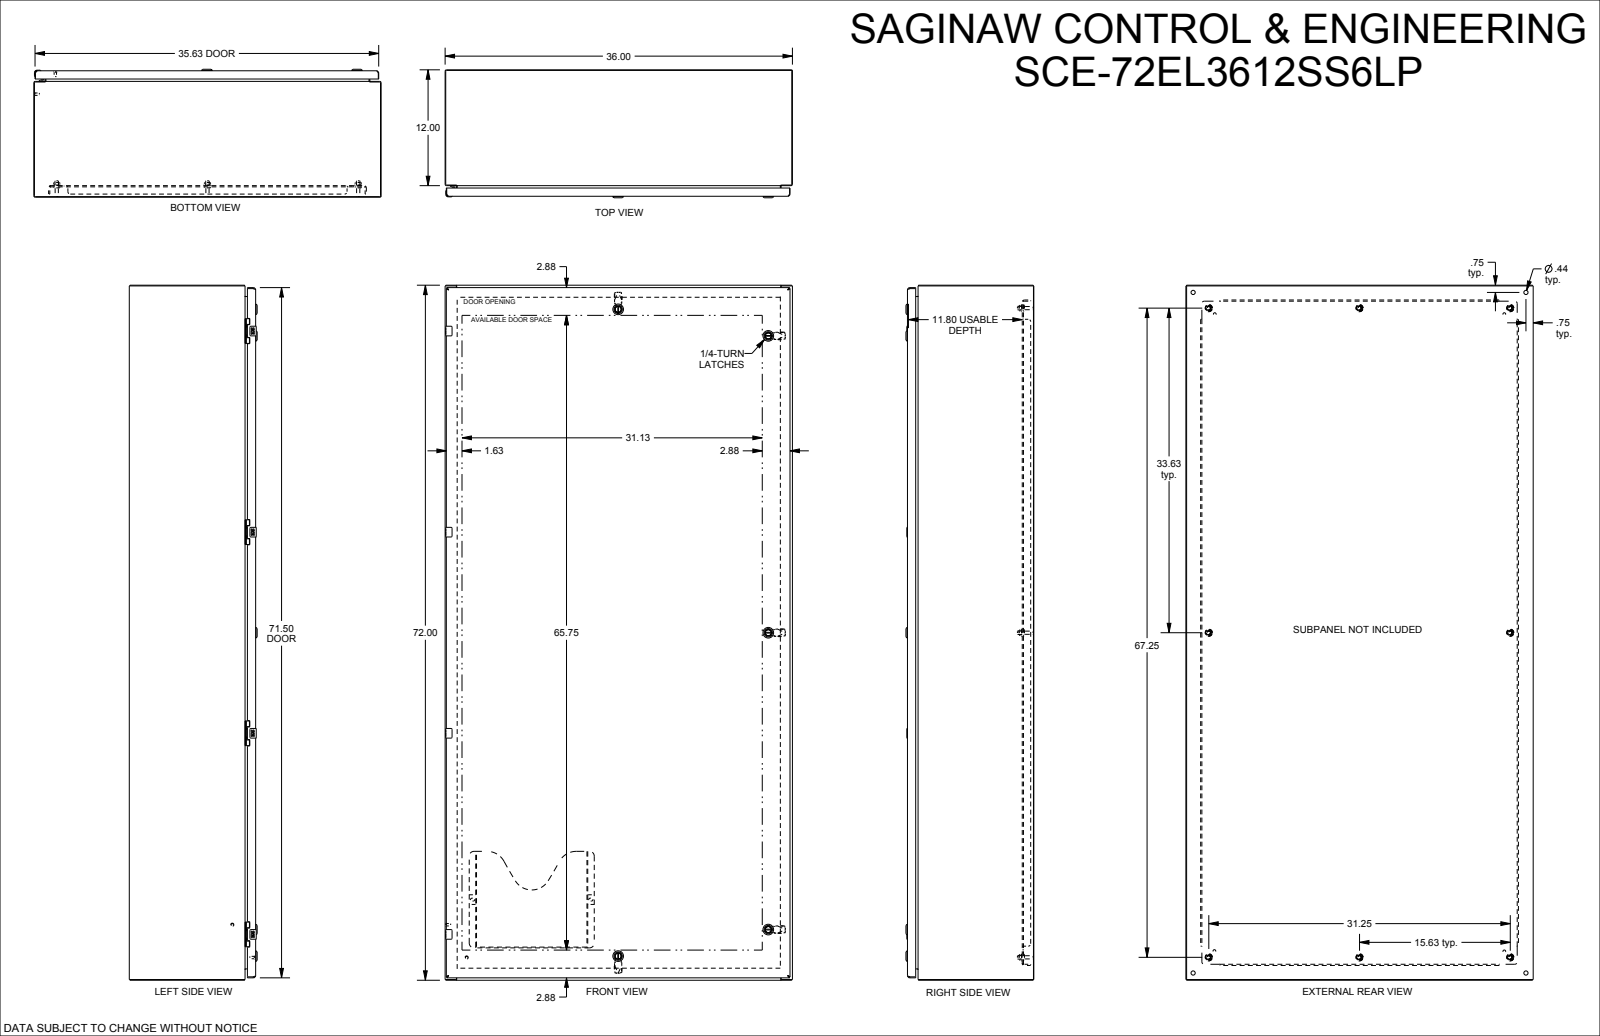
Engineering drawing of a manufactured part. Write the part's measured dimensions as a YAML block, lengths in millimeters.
part_name: "SCE-72EL3612SS6LP"
step_written_by: "SolidWorks 2019 (CONFIG_CONTROL_DESIGN)"
units: millimeters
bodies: {solids: 0, faces: 5420, planar: 2661, cylindrical: 1535, other: 1224}
overall_size: [1828.8, 914.4, 336.7]
round_holes:
  - {diameter: 10, count: 15}
  - {diameter: 4.4, count: 8}
  - {diameter: 5.2, count: 8}
  - {diameter: 6.2, count: 8}
  - {diameter: 6.8, count: 8}
  - {diameter: 9.3, count: 8}
  - {diameter: 9.5, count: 8}
  - {diameter: 12.7, count: 8}
  - {diameter: 5, count: 5}
  - {diameter: 8, count: 5}
  - {diameter: 16.1, count: 5}
  - {diameter: 4, count: 4}
round_bosses_or_shafts:
  - {diameter: 4.3, count: 12}
  - {diameter: 9.3, count: 8}
  - {diameter: 8.4, count: 8}
  - {diameter: 6.4, count: 8}
  - {diameter: 28, count: 5}
  - {diameter: 22, count: 5}
  - {diameter: 20.4, count: 5}
  - {diameter: 19.8, count: 5}
partial_cylinders:
  - {radius: 0.3, count: 142}
  - {radius: 0.3, count: 52}
  - {radius: 0.5, count: 52}
  - {radius: 0.4, count: 48}
  - {radius: 1, count: 23}
  - {radius: 4, count: 20}
  - {radius: 0.8, count: 17}
  - {radius: 0.8, count: 16}
face_to_face_distances: [1.9, 2.6, 328.2, 330.1, 25.4, 332.7, 330.8, 28.6, 299.6, 302.8]
hole_center_spacings: [62.5, 529.2, 1058.3, 32.4, 120.8, 88.4, 108.3, 529.2]
